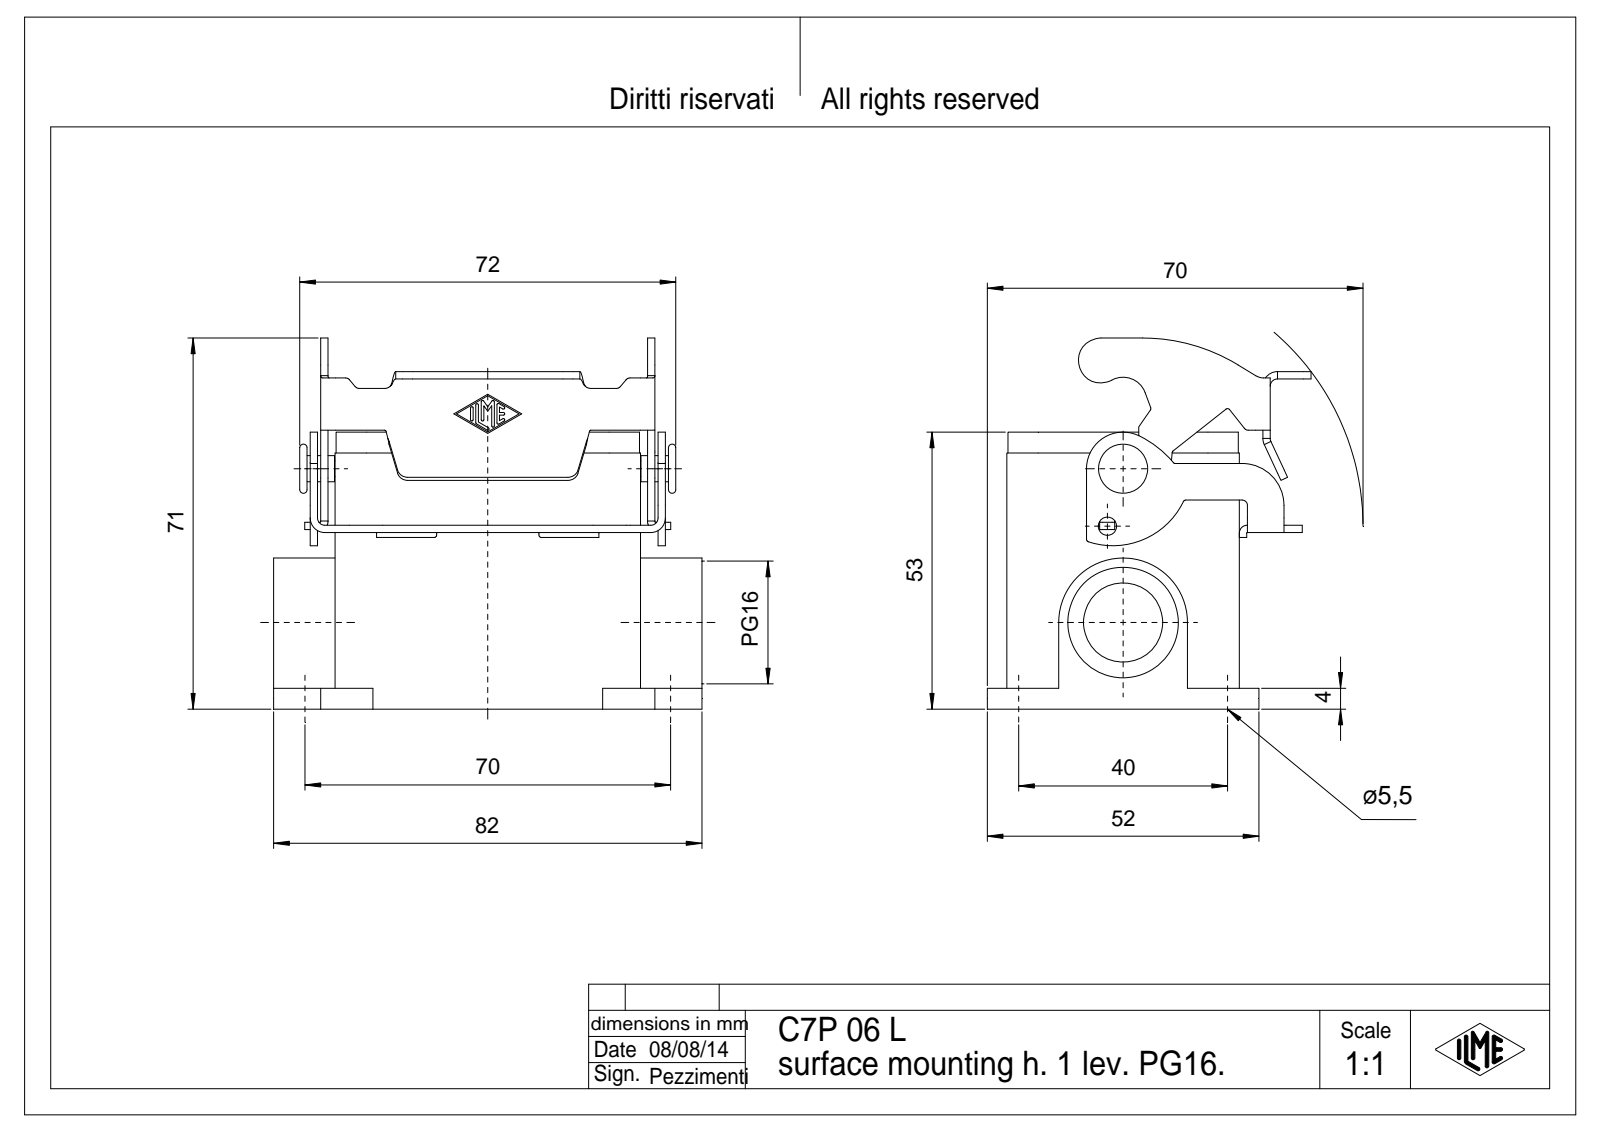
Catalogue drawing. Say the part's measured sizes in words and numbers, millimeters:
The part is named "p1; p2; CVP_06_L; C7P_06_L.stp". Its 3-D file was written by "Creo Elements/Direct Modeling 18.0B 02-Dec-2011 (C) Parametric Technology GmbH (AUTOMOTIVE_DESIGN)". It is 2 solids with 397 faces: 199 planar, 176 cylindrical and 22 other. Overall it measures 82 by 71 by 61.98 millimeters. Its volume is 72 125 cubic millimeters and its surface area 39 187 square millimeters. Round holes: 4 of diameter 2.46, 4 of diameter 3, 4 of diameter 5.5, 1 of diameter 3.5, 1 of diameter 15.16, 1 of diameter 21.16. Round bosses or shafts: 1 of diameter 5, 1 of diameter 3.2, 1 of diameter 3. Partial cylindrical surfaces (rounded edges, fillets, slot ends): 16 of radius 0.25, 12 of radius 0.5, 12 of radius 1, 11 of radius 1.5, 8 of radius 2, 6 of radius 1.4, 6 of radius 2.8, 4 of radius 1.8. The main face-to-face distances are 4, 40.5, 1.4, 44.5, 2, 64.6, 6.75, 36.5, 50.5, 2.75. The hole center spacings are 14.53, 35.93, 57.37, 66.12, 27, 40, 44, 51.62.
